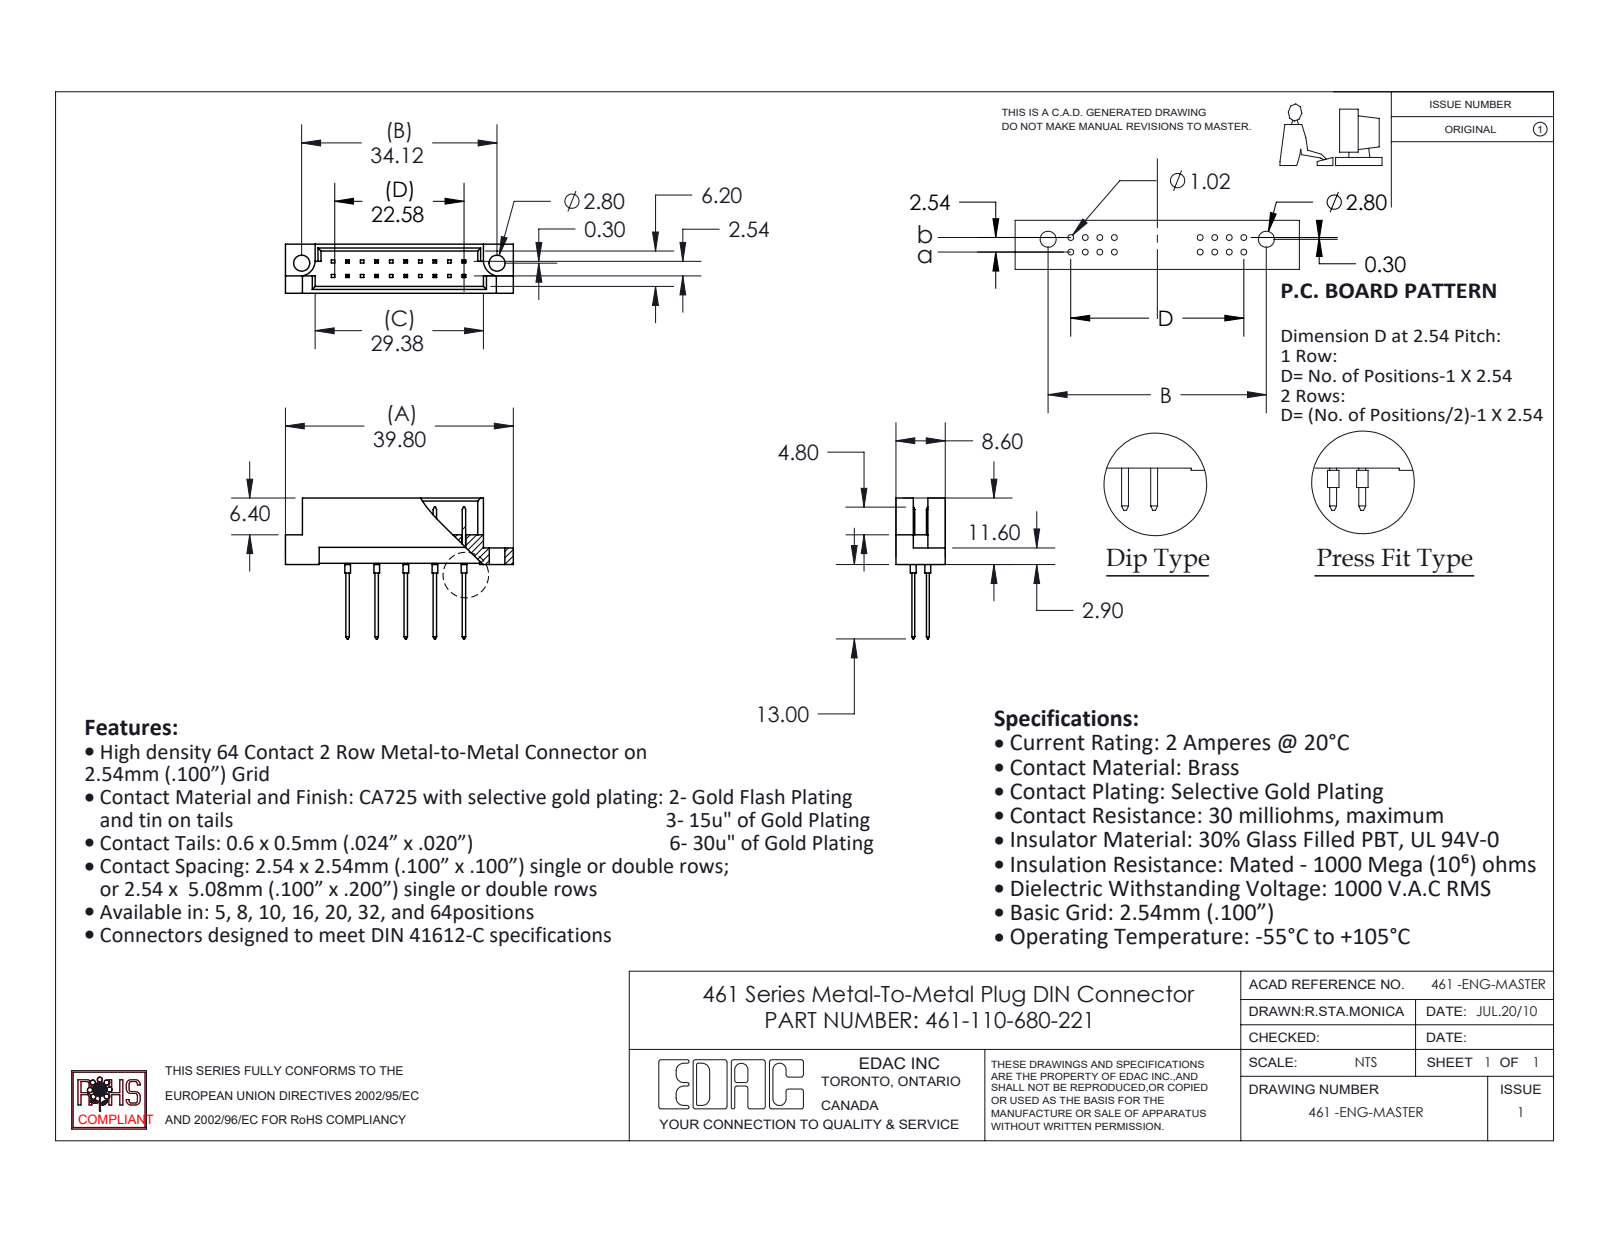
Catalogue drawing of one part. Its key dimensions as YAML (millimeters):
part_name: "461 Part_20; 461-290_80; 461-110-680-221"
step_written_by: "SolidWorks 2020 (CONFIG_CONTROL_DESIGN)"
units: millimeters
bodies: {solids: 11, faces: 348, planar: 322, cylindrical: 26, other: 0}
overall_size: [39.8, 24.6, 8.6]
volume: 1980
surface_area: 2864
round_holes:
  - {diameter: 2.8, count: 2}
round_bosses_or_shafts:
  - {diameter: 1, count: 10}
partial_cylinders:
  - {radius: 2.8, count: 2}
face_to_face_distances: [1.2, 7.4, 8.6, 6.2, 5.08, 2.54, 2.78, 3.28, 5.32, 5.82]
hole_center_spacings: [34.12]
